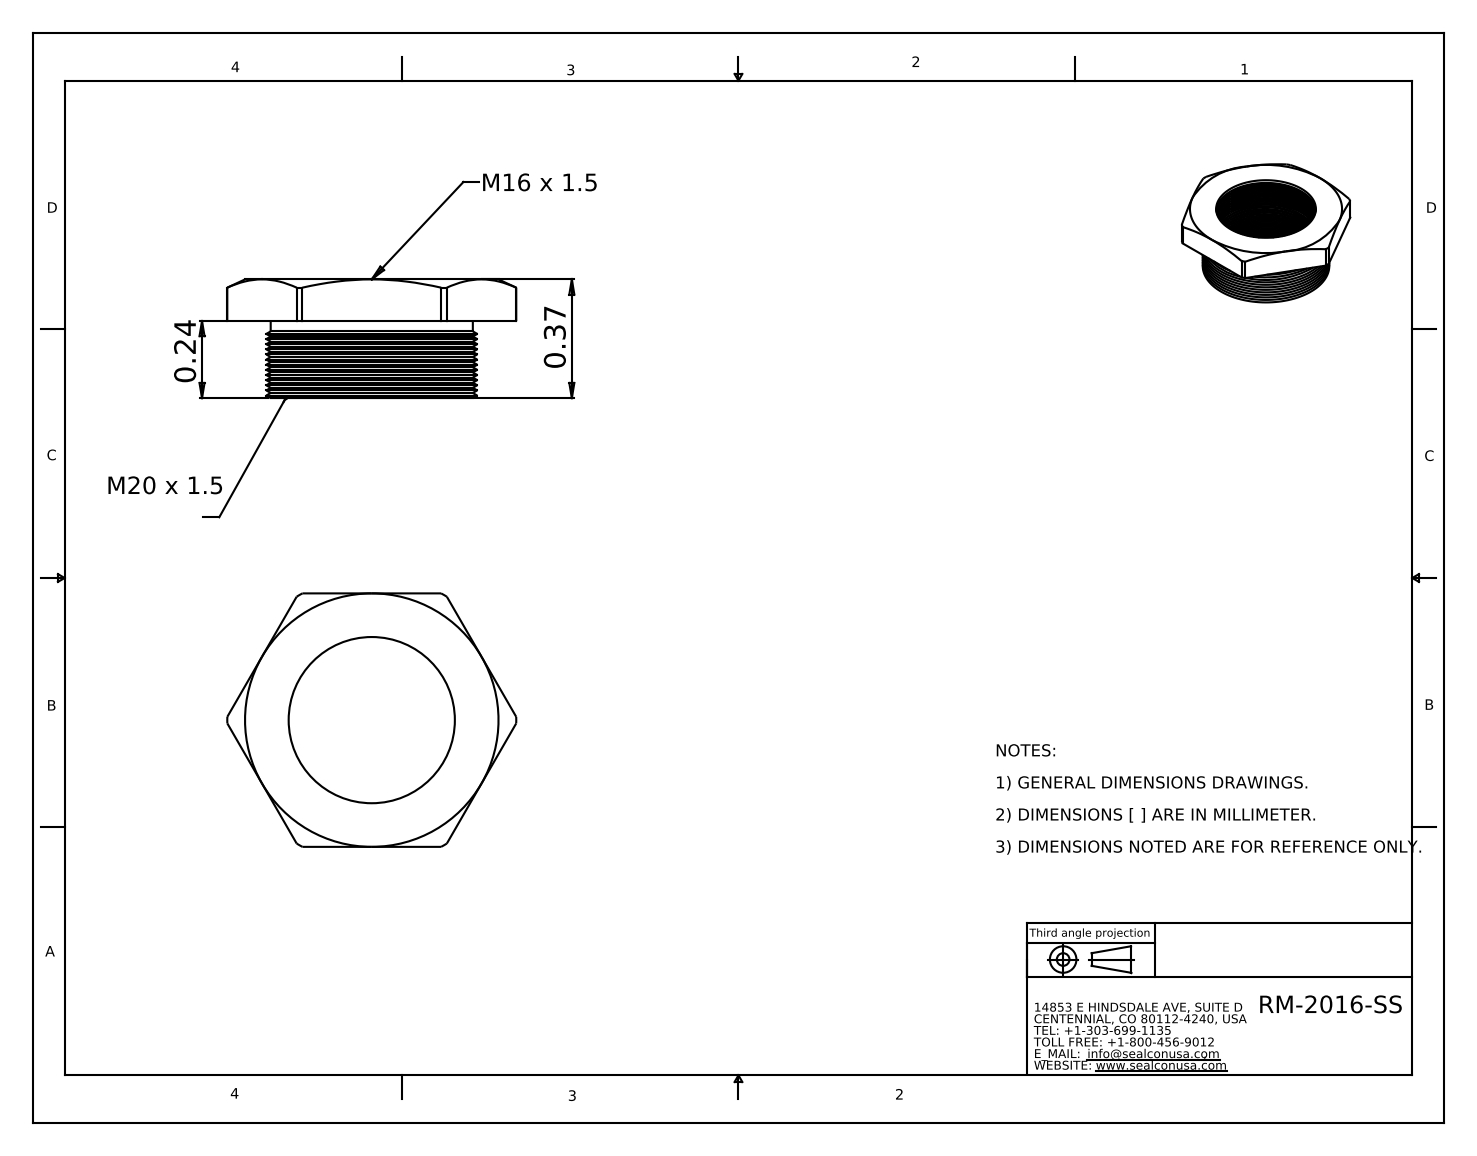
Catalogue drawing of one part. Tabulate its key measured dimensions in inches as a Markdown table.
| quantity | value |
| --- | --- |
| part name | RM-2016-SS |
| STEP written by | SolidWorks 2008 (CONFIG_CONTROL_DESIGN) |
| units | inches |
| bodies | 1 solid, 241 faces (9 planar, 81 cylindrical, 151 other) |
| overall size | 0.901 × 0.79 × 0.37 |
| volume | 0.068 in³ |
| surface area | 3.098 in² |
| round holes (diameter × count) | 0.518 × 1 |
| round bosses / shafts (diameter × count) | 0.63 × 1 |
| partial cylindrical surfaces (radius × count) | 0.45 × 1 |
| main face-to-face distances | 0.13, 0.79, 0.24, 0.37 |
